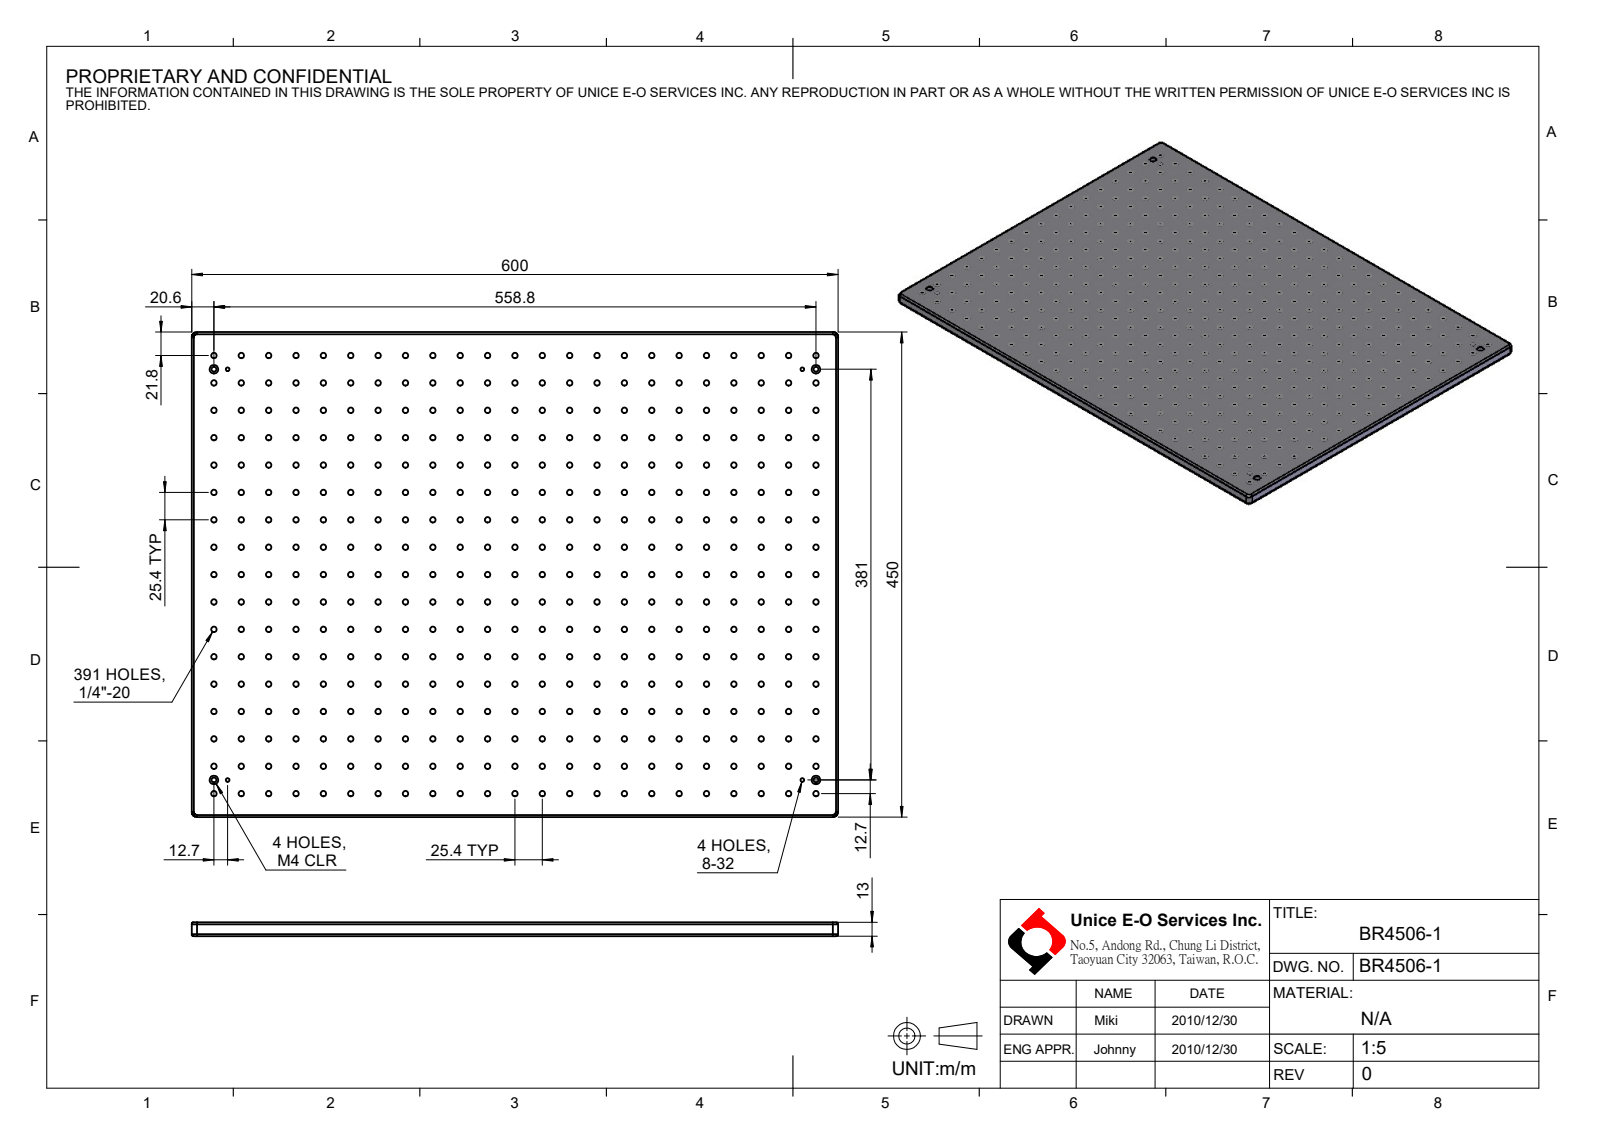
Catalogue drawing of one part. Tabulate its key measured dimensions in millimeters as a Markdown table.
| quantity | value |
| --- | --- |
| part name | BR4506-1 |
| STEP written by | SolidWorks 2016 (CONFIG_CONTROL_DESIGN) |
| units | millimeters |
| bodies | 1 solid, 836 faces (10 planar, 818 cylindrical, 8 other) |
| overall size | 600 × 450 × 13 |
| volume | 3 400 000 mm³ |
| surface area | 630 430 mm² |
| round holes (diameter × count) | 5.11 × 391, 3.45 × 4, 4.5 × 4, 8 × 4 |
| partial cylindrical surfaces (radius × count) | 2 × 8, 5 × 4 |
| main face-to-face distances | 13, 450, 600, 7, 6 |
| hole center spacings | 25.4, 50.8, 76.2, 127, 101.6, 152.4, 177.8, 203.2 |
